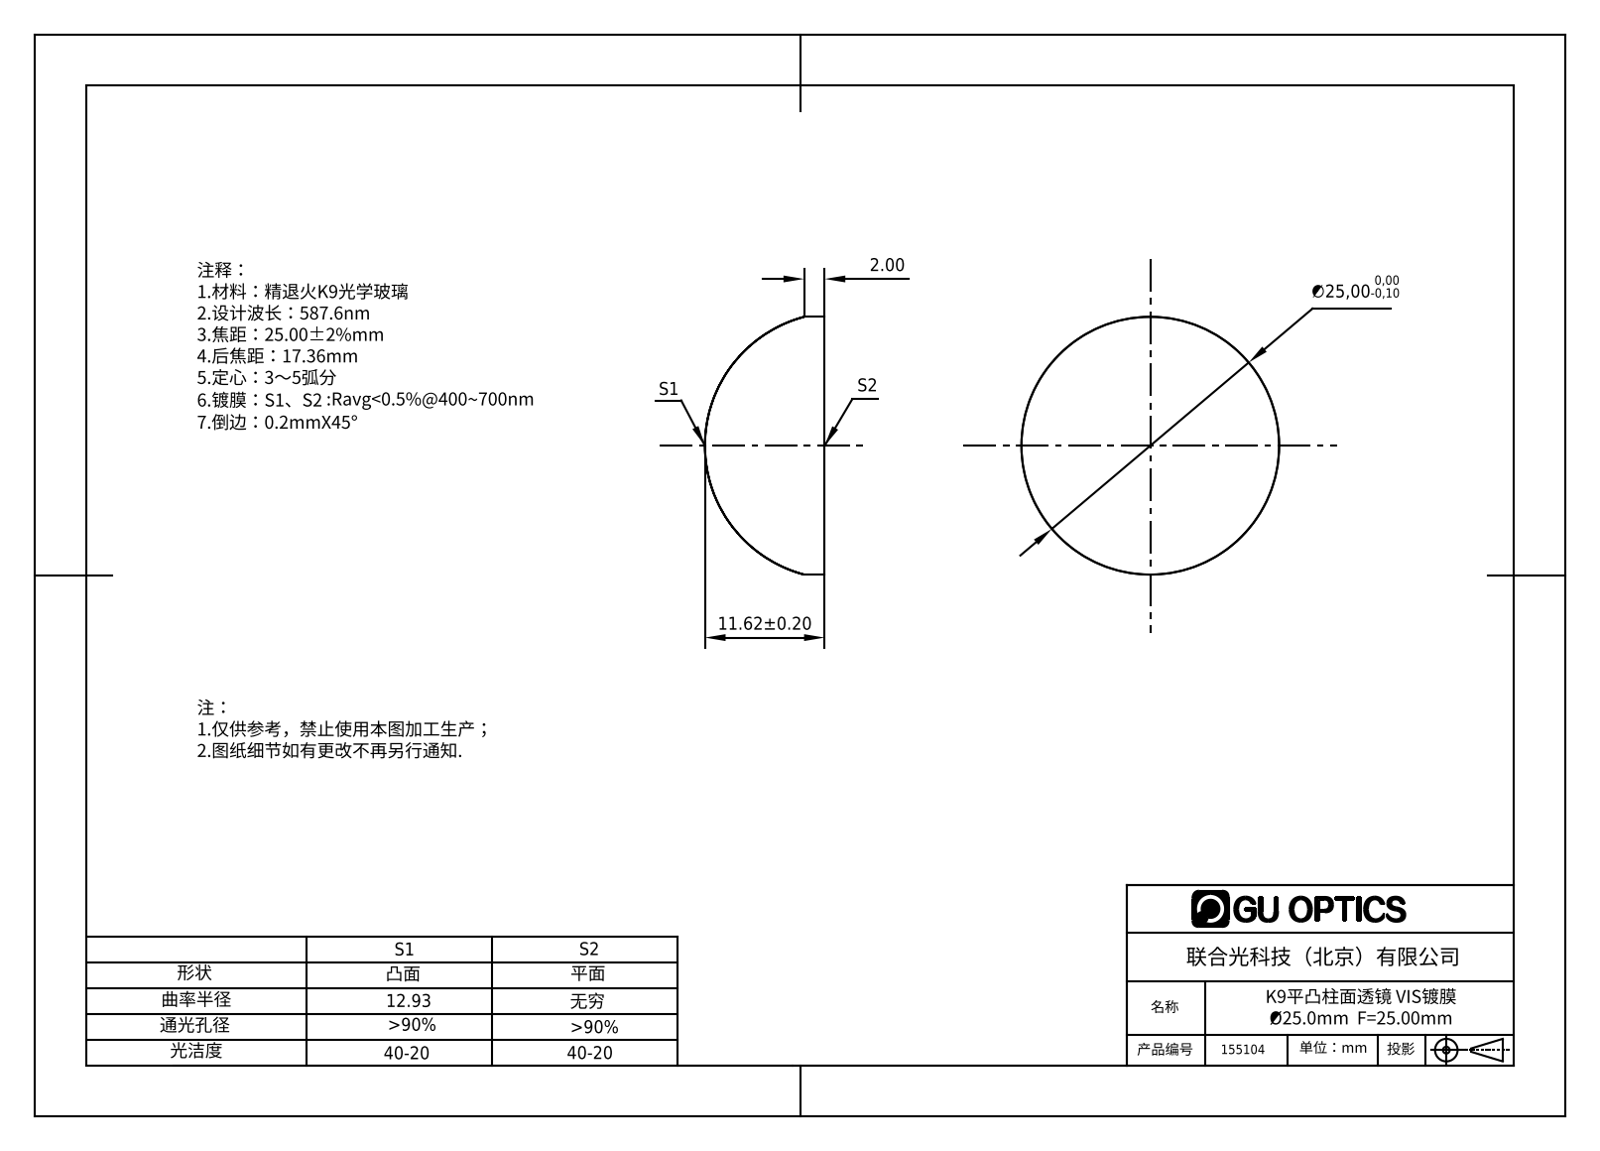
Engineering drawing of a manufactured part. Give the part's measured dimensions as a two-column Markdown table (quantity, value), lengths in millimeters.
| quantity | value |
| --- | --- |
| part name | 155038 |
| STEP written by | SolidWorks 2016 (AUTOMOTIVE_DESIGN) |
| units | millimeters |
| bodies | 1 solid, 4 faces (1 planar, 3 cylindrical, 0 other) |
| overall size | 25 × 25 × 11.62 |
| volume | 4 827 mm³ |
| surface area | 1 680 mm² |
| round bosses / shafts (diameter × count) | 25 × 1 |
| partial cylindrical surfaces (radius × count) | 12.93 × 1 |
